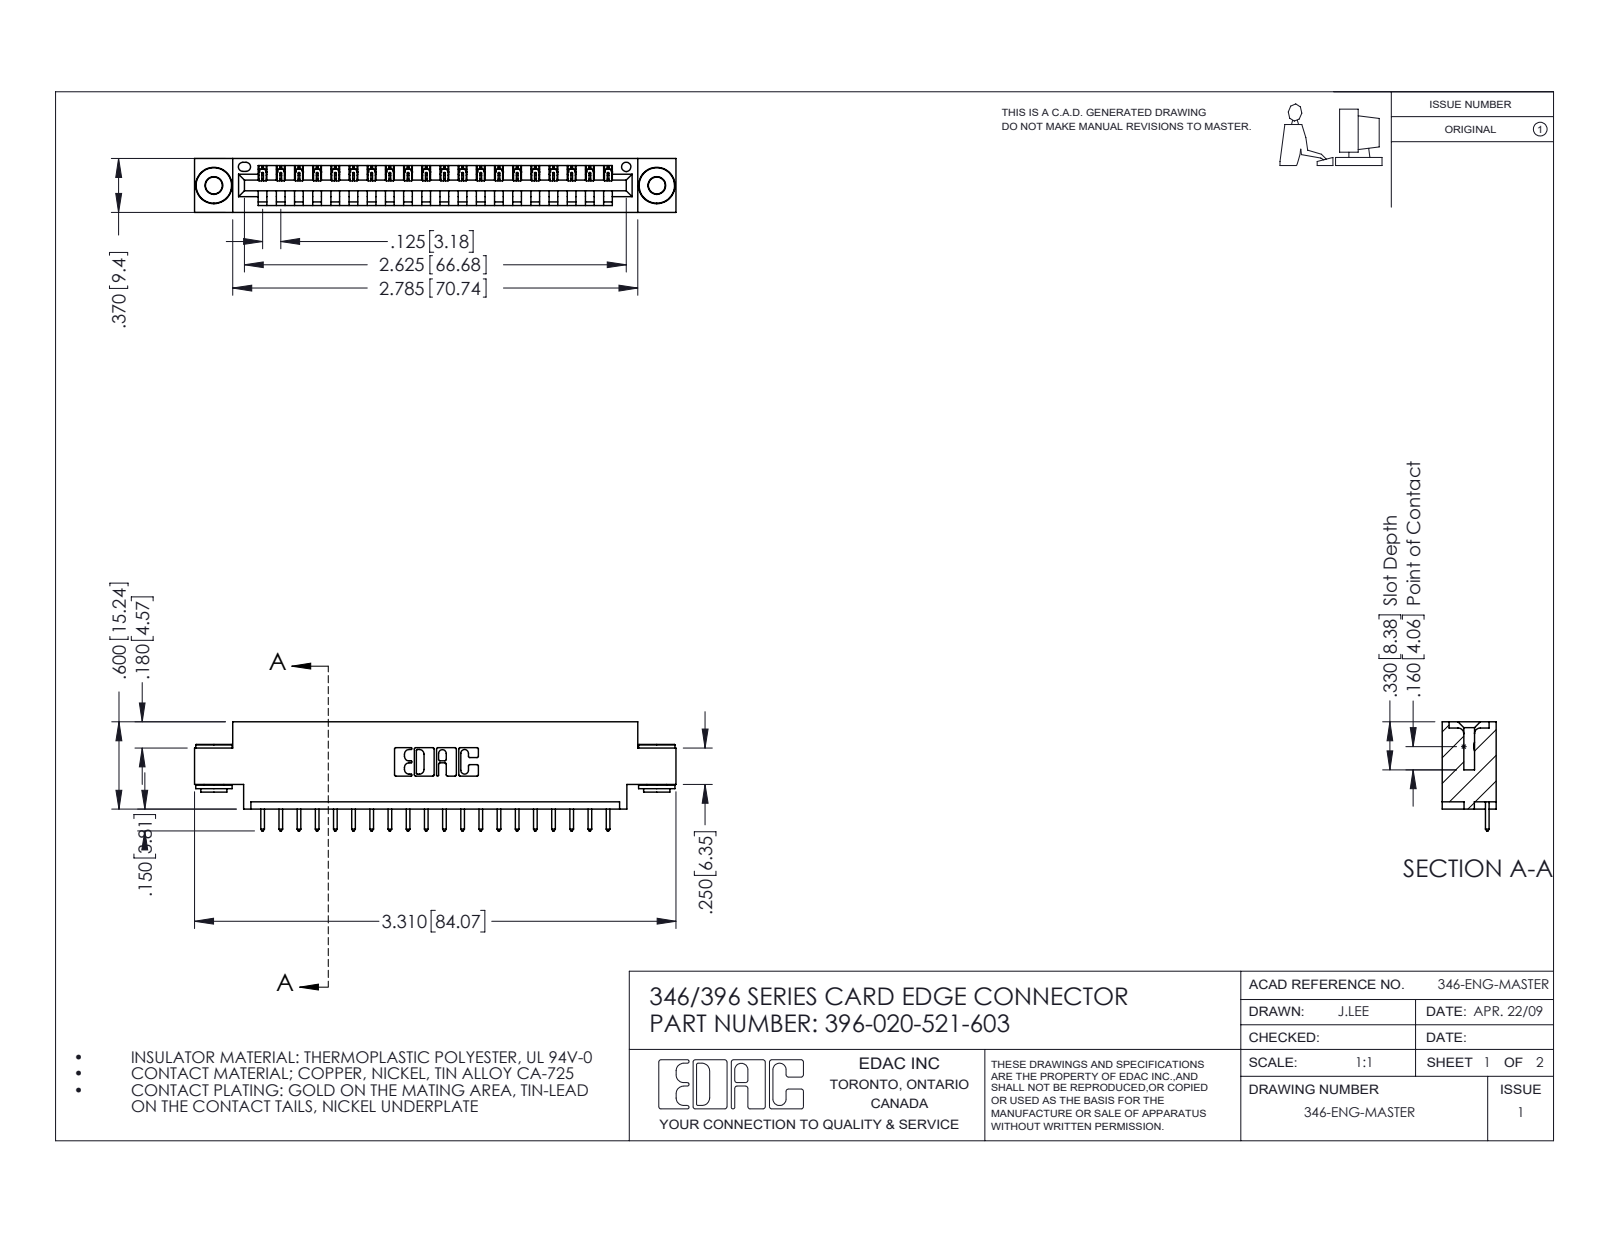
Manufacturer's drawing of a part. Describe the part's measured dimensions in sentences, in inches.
The part is named "346 Part_0.170 Offset - 0.156 Dia-TH; 345-292-001_345-293-121; 396-020-521-603; 345-250-002_345-250-002-102". Its 3-D file was written by "SolidWorks 2016 (CONFIG_CONTROL_DESIGN)". It is 23 solids with 1324 faces: 890 planar, 426 cylindrical and 8 other. Overall it measures 3.31 by 0.75 by 0.37 inches. Its volume is 0.47 cubic inches and its surface area 14.79 square inches. Round holes: 2 of diameter 0.116, 2 of diameter 0.156, 1 of diameter 0.064. Round bosses or shafts: 2 of diameter 0.25, 2 of diameter 0.18, 2 of diameter 0.136. Partial cylindrical surfaces (rounded edges, fillets, slot ends): 40 of radius 0.006, 40 of radius 0.01, 22 of radius 0.01, 6 of radius 0.007, 6 of radius 0.031, 3 of radius 0.026, 2 of radius 0.031, 2 of radius 0.04. The main face-to-face distances are 0.37, 0.048, 0.322, 0.25, 0.025, 0.072, 0.298, 0.148, 0.222, 0.1. The hole center spacings are 0.246, 2.837, 3.045.
